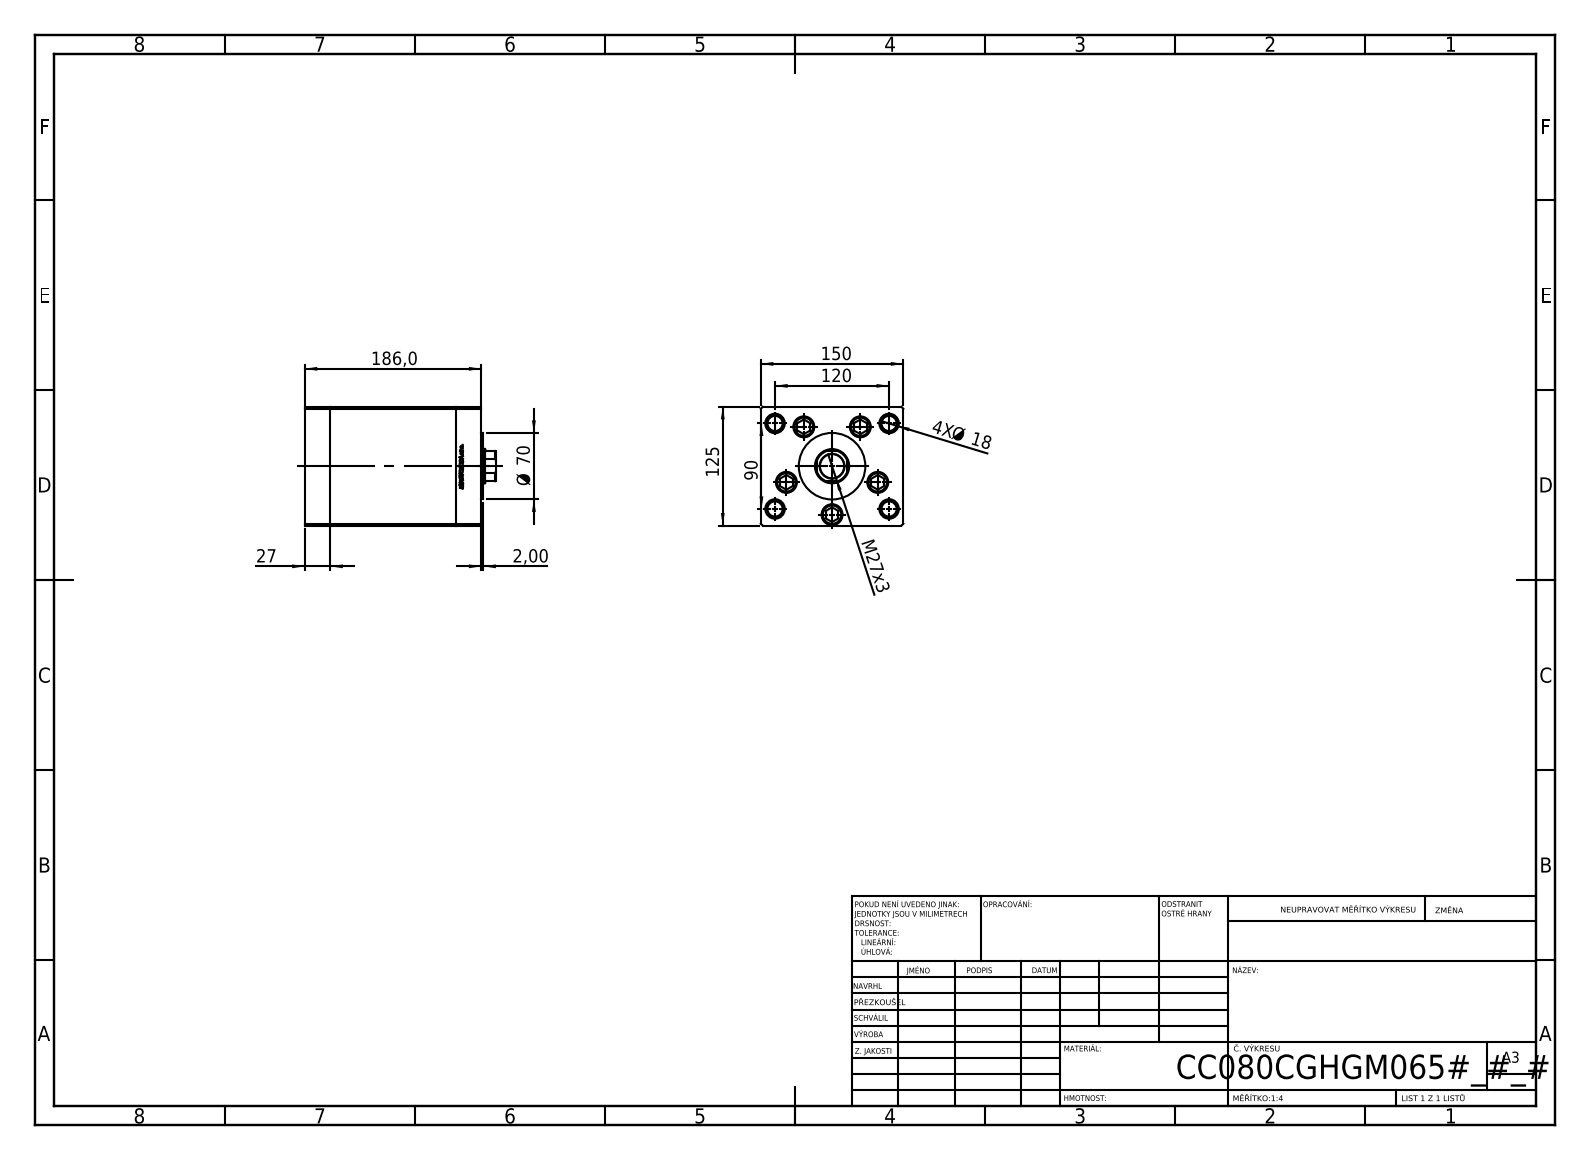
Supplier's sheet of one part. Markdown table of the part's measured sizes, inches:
| quantity | value |
| --- | --- |
| part name | V220C_C MIDDLE; V220C_VC_C; V220C BACK_C; V220C FRONT (+1 more) |
| STEP written by | SolidWorks 2019 (CONFIG_CONTROL_DESIGN) |
| units | inches |
| bodies | 13 solids, 1186 faces (545 planar, 179 cylindrical, 462 other) |
| overall size | 7.913 × 5.906 × 4.921 |
| volume | 177.9 in³ |
| surface area | 562.6 in² |
| round holes (diameter × count) | 0.689 × 9, 0.866 × 5, 0.079 × 4, 0.518 × 4, 0.63 × 4, 0.807 × 4, 0.827 × 1, 1.004 × 1, 1.417 × 1 |
| round bosses / shafts (diameter × count) | 0.315 × 5, 0.827 × 4, 3.15 × 1, 2.756 × 1 |
| partial cylindrical surfaces (radius × count) | 0.037 × 2, 0.689 × 1 |
| main face-to-face distances | 1.063, 6.26, 5.197, 5.906, 4.921, 1.319, 7.323, 0.256, 6.004, 4.941 |
| hole center spacings | 2.008, 2.953, 1.198, 1.2, 2.319, 2.374, 2.411, 2.486 |
